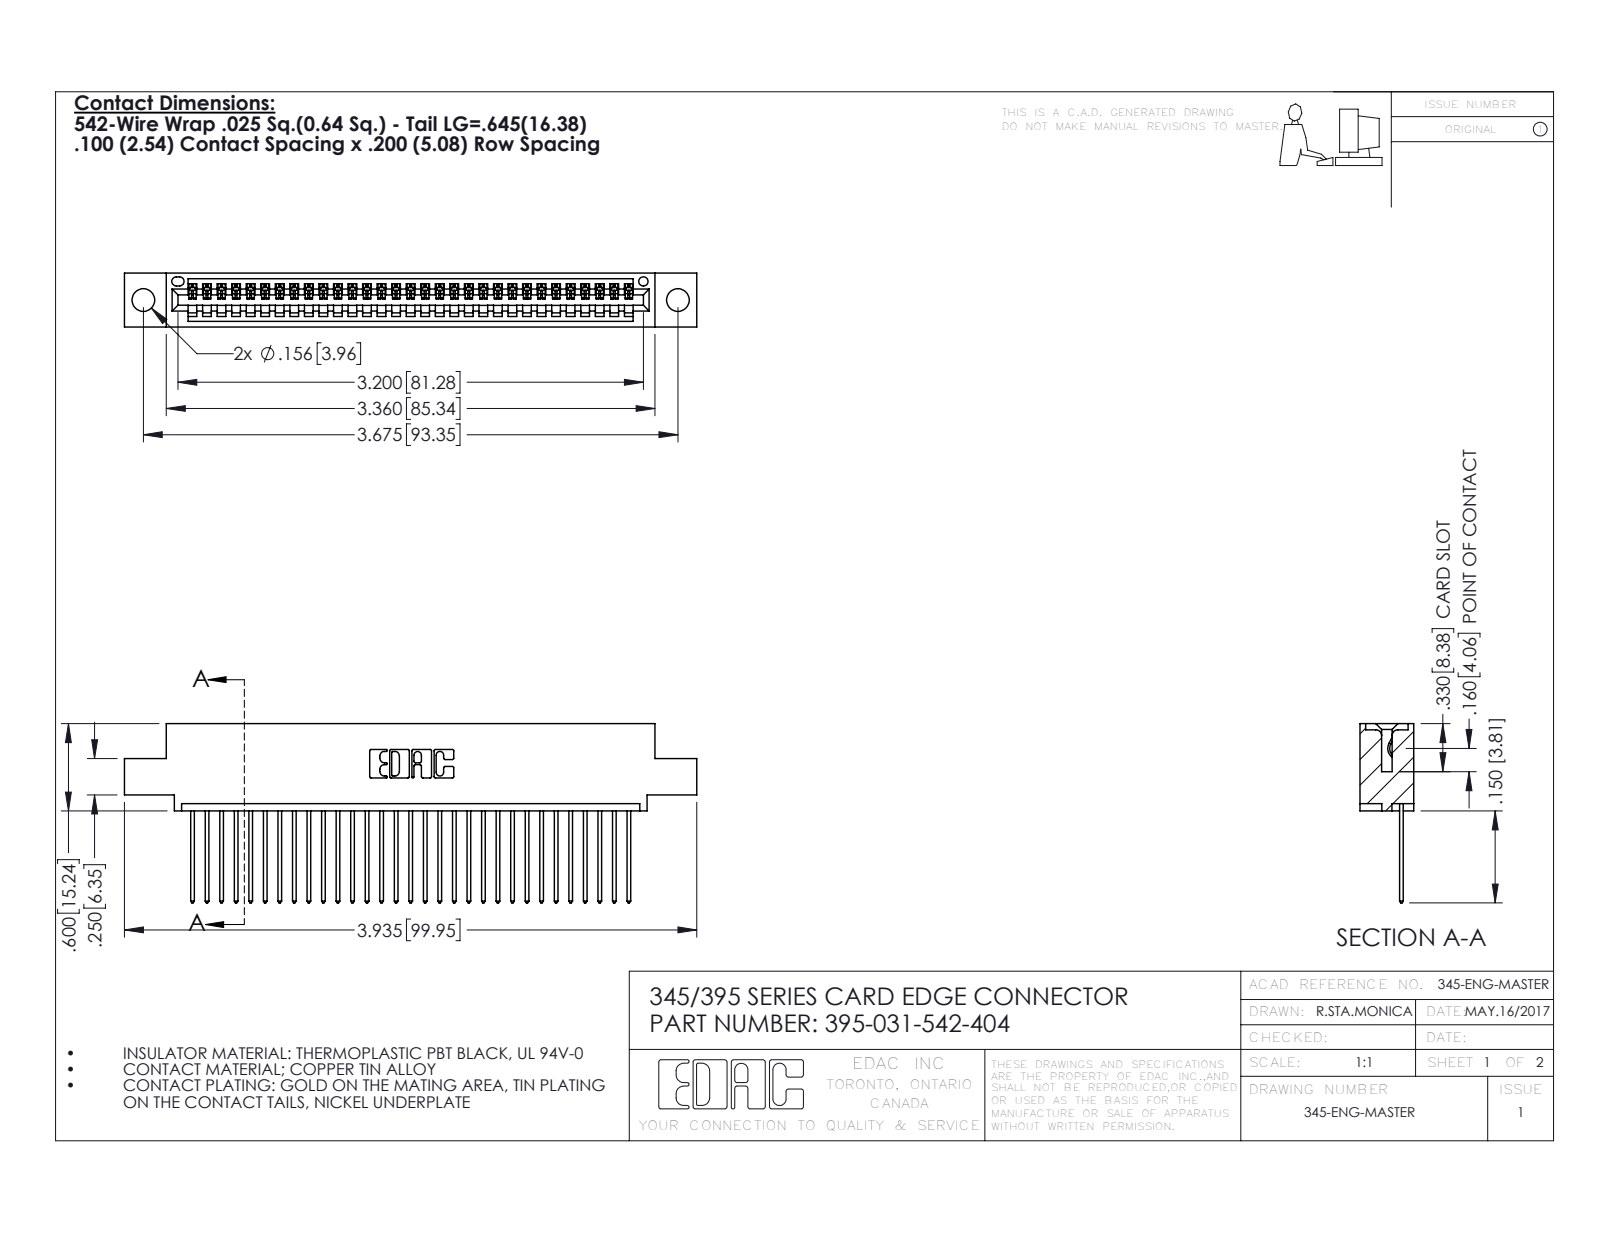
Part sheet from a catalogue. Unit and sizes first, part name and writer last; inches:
Units: inches
Overall size (bounding box): 3.935 × 1.232 × 0.37
Round holes (diameter × count): ⌀0.156 ×2, ⌀0.064 ×1
Partial cylindrical surfaces — rounded edges, fillets, slot ends (radius × count): R0.006 ×62, R0.01 ×62, R0.01 ×22, R0.007 ×6, R0.031 ×6, R0.026 ×3, R0.031 ×2, R0.04 ×2
Main face-to-face distances: 0.298, 0.072, 0.37, 0.2, 0.098, 0.272, 0.025, 0.225, 0.149, 0.072
Hole centre spacings: 0.27, 3.44, 3.675
Volume: 0.568 in³ · Surface area: 19.45 in²
Bodies: 32 solids, 1928 faces (1324 planar, 604 cylindrical, 0 other)
Part name (STEP PRODUCT): 345-292-001_345-293-142; 345 Part_0.110 Offset - 0.156 Dia-TH; 395-031-542-404
STEP written by: SolidWorks 2016 (CONFIG_CONTROL_DESIGN)
